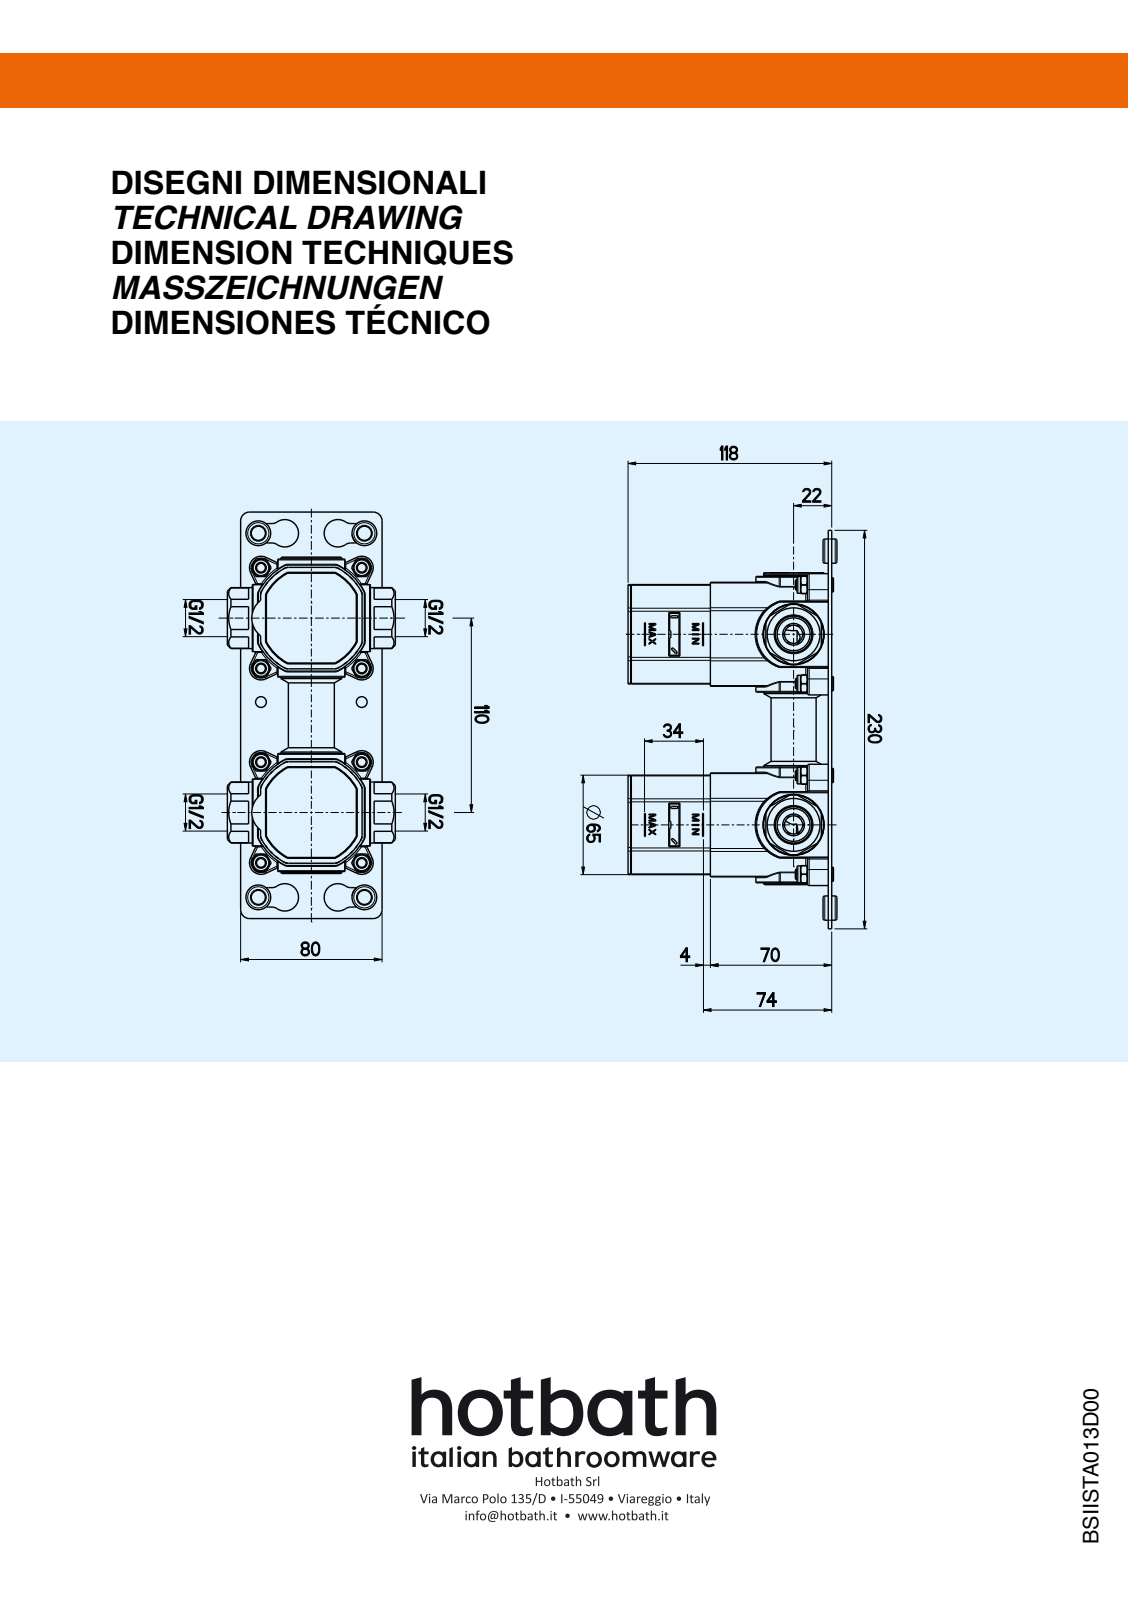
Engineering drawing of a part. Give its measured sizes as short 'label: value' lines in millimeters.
name: AF009EXT-00; BSIMVXA013_1_oa_0; BSIMVXA014_1; ABIX005C018 (+8 more)
written by: Solid Edge (AUTOMOTIVE_DESIGN)
unit: mm
bodies: 10 solids, 458 faces (233 planar, 88 cylindrical, 137 other)
size: 182 × 72 × 63.81
volume: 70 194 mm³; area: 55 185 mm²
holes: 3× ⌀2.5, 3× ⌀4, 2× ⌀35.5, 2× ⌀41, 2× ⌀44.8, 2× ⌀69.5, 1× ⌀3.2, 1× ⌀4.2, 1× ⌀6, 1× ⌀7, 1× ⌀7.1, 1× ⌀8.1
bosses: 2× ⌀72, 2× ⌀50, 1× ⌀40, 1× ⌀38, 1× ⌀37.3, 1× ⌀37, 1× ⌀34.5, 1× ⌀8
rounds: 12× R0.1, 4× R0.4, 2× R0.56, 2× R0.73, 2× R1.6, 2× R2.3, 1× R0.49, 1× R0.62
face distances: 2.3, 5, 2.7, 56.11, 53.41, 51.11, 63.82, 61.12, 58.82, 7.71
hole spacings: 17, 5.02, 5.03, 9.94, 12, 13.5, 15.4, 21.5
